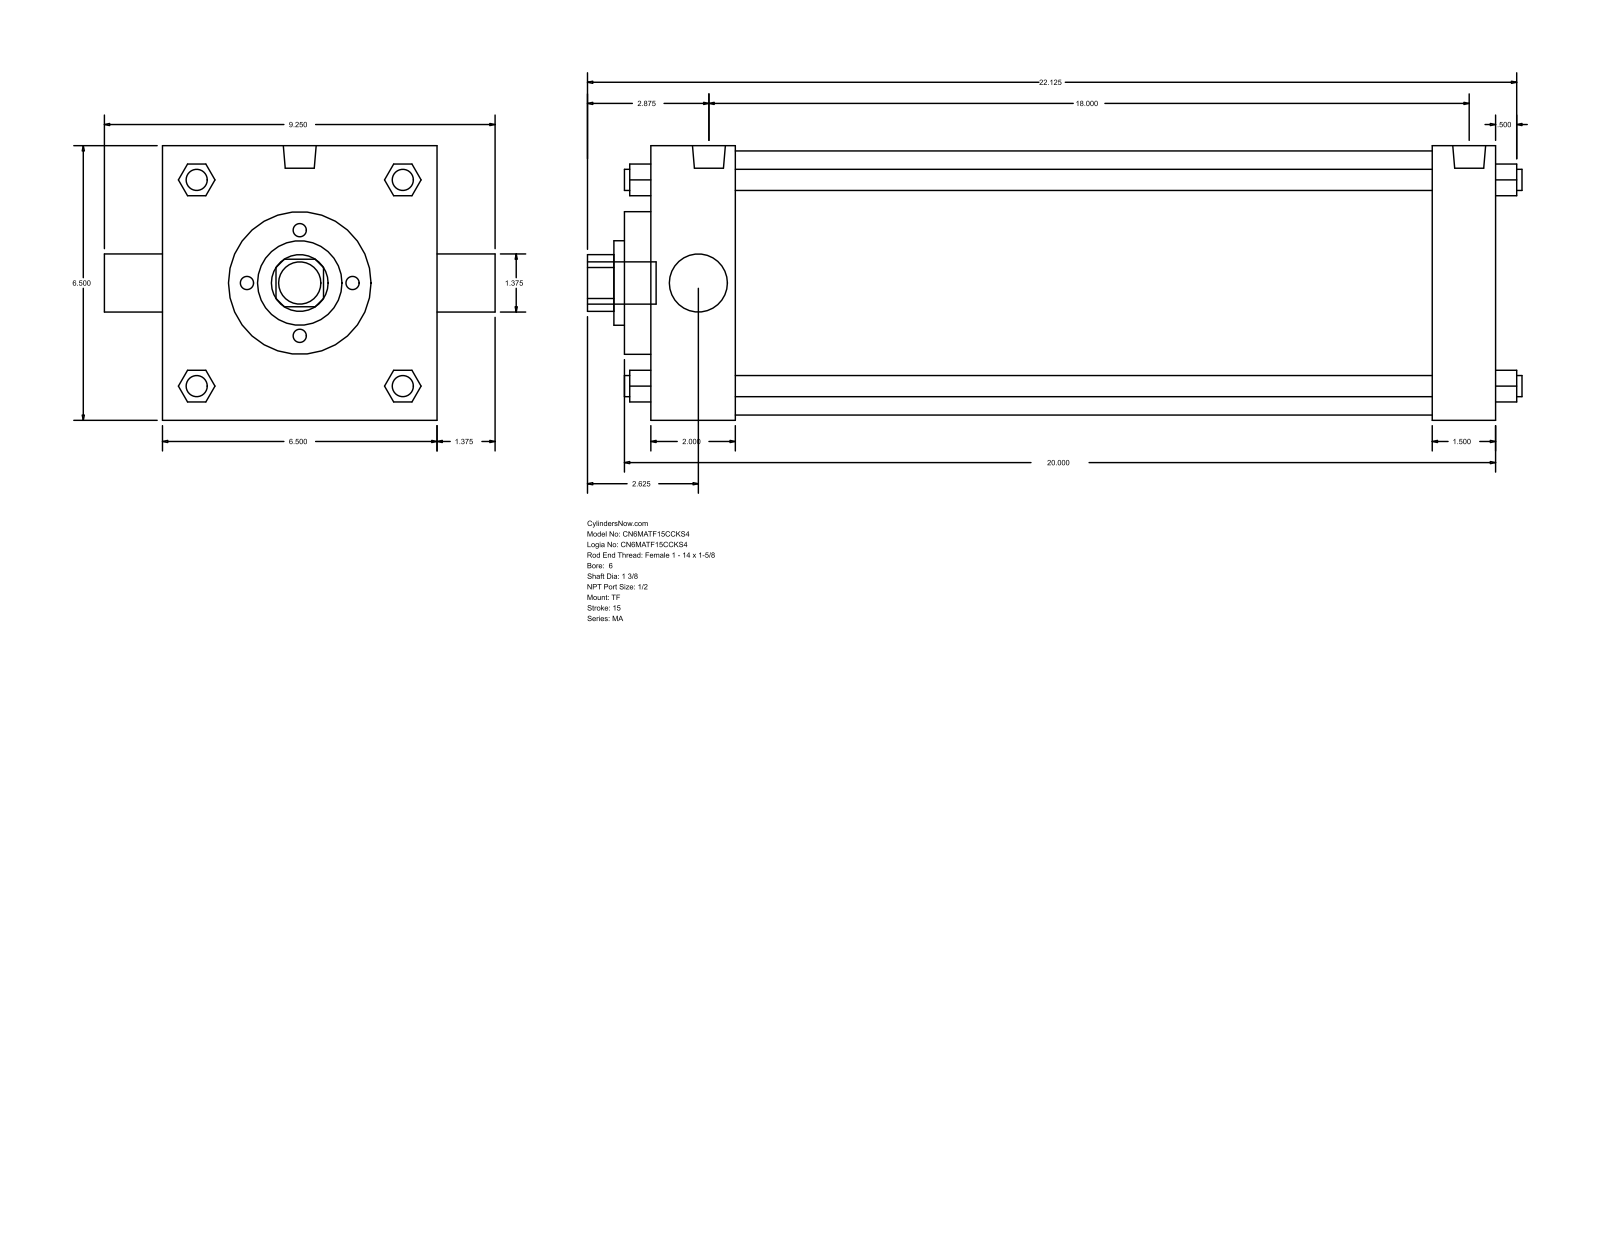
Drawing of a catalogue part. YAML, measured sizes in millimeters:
part_name: "MA_TF__0600_1.375"
step_written_by: "GSSL Pune (CONFIG_CONTROL_DESIGN)"
units: millimeters
bodies: {solids: 0, faces: 122, planar: 93, cylindrical: 29, other: 0}
overall_size: [561.98, 234.95, 165.1]
round_holes:
  - {diameter: 34.92, count: 2}
  - {diameter: 50.8, count: 1}
  - {diameter: 85.72, count: 1}
  - {diameter: 158.75, count: 1}
round_bosses_or_shafts:
  - {diameter: 12.7, count: 4}
  - {diameter: 17.46, count: 3}
  - {diameter: 19.77, count: 2}
  - {diameter: 25.4, count: 1}
partial_cylinders:
  - {radius: 17.06, count: 1}
face_to_face_distances: [165.1, 511.17, 50.8, 473.08, 460.37, 422.28, 38.09, 15.87, 66.67, 488.95]
